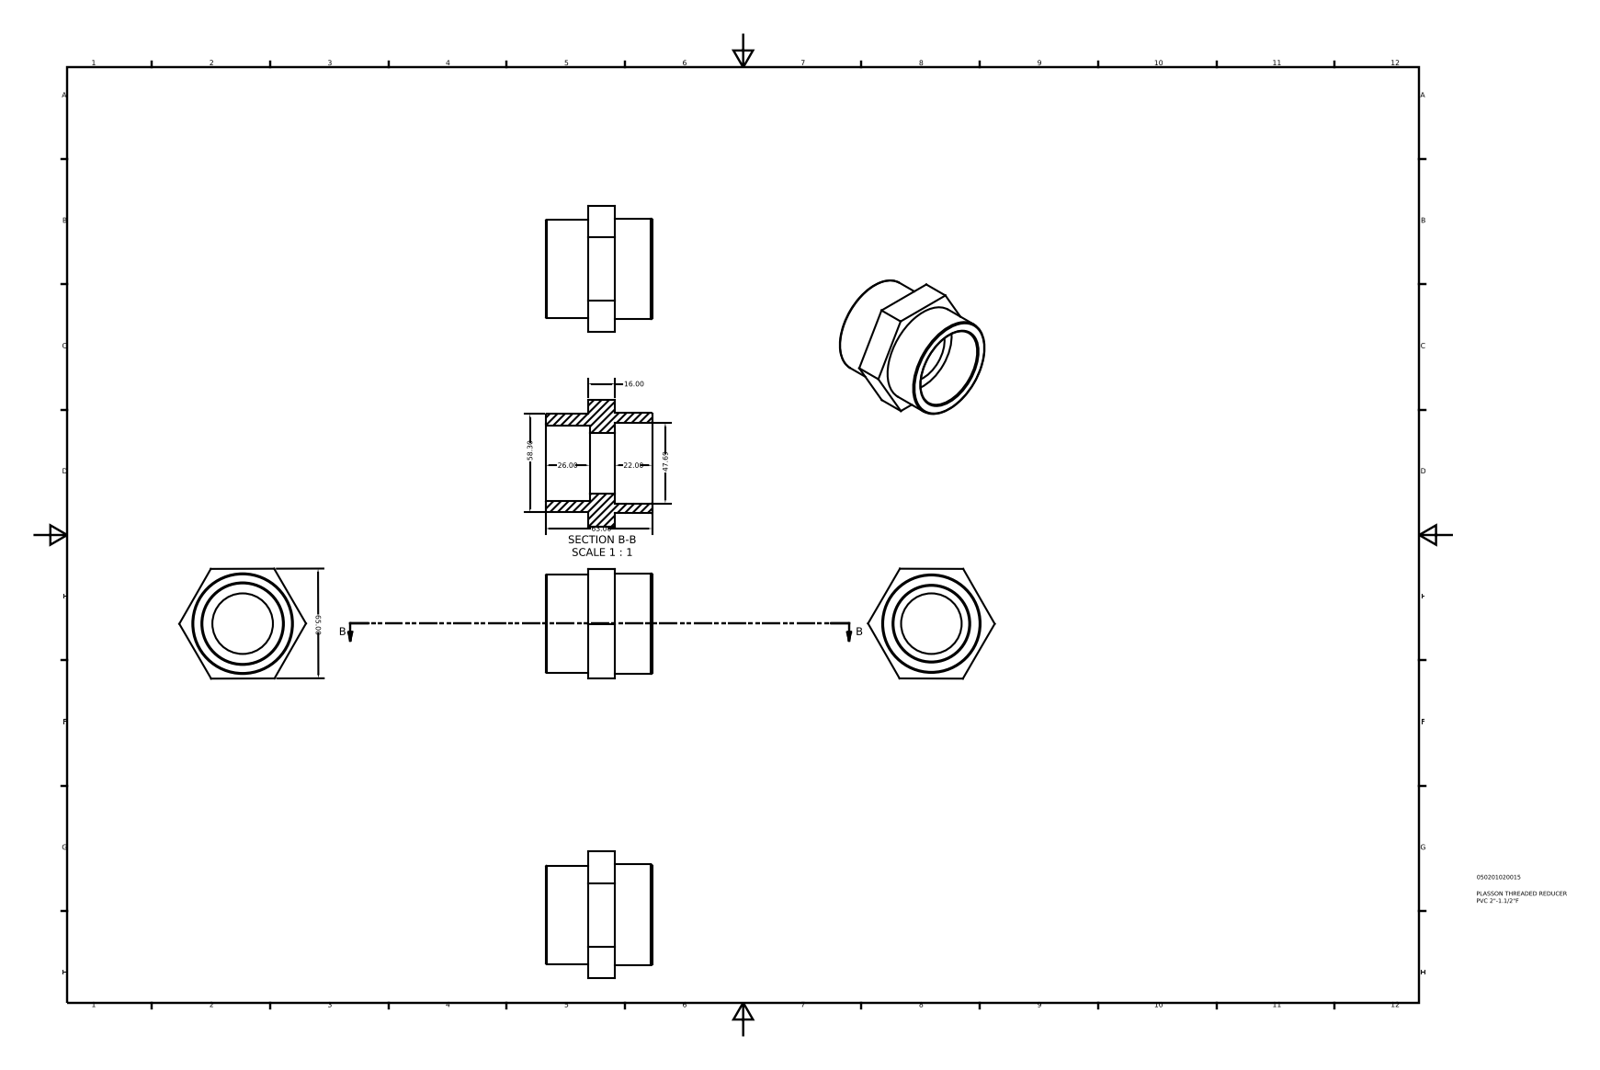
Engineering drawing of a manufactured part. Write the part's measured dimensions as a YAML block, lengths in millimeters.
part_name: "050201020015"
step_written_by: "Autodesk Inventor 2015 (AUTOMOTIVE_DESIGN)"
units: millimeters
bodies: {solids: 1, faces: 21, planar: 12, cylindrical: 5, other: 4}
overall_size: [75.06, 65.11, 63]
volume: 91103
surface_area: 26078
round_holes:
  - {diameter: 35.88, count: 1}
  - {diameter: 44.84, count: 1}
  - {diameter: 47.69, count: 1}
round_bosses_or_shafts:
  - {diameter: 59.61, count: 1}
  - {diameter: 58.3, count: 1}
face_to_face_distances: [65.04, 16, 25, 41, 63, 38, 22, 65, 26, 1]
